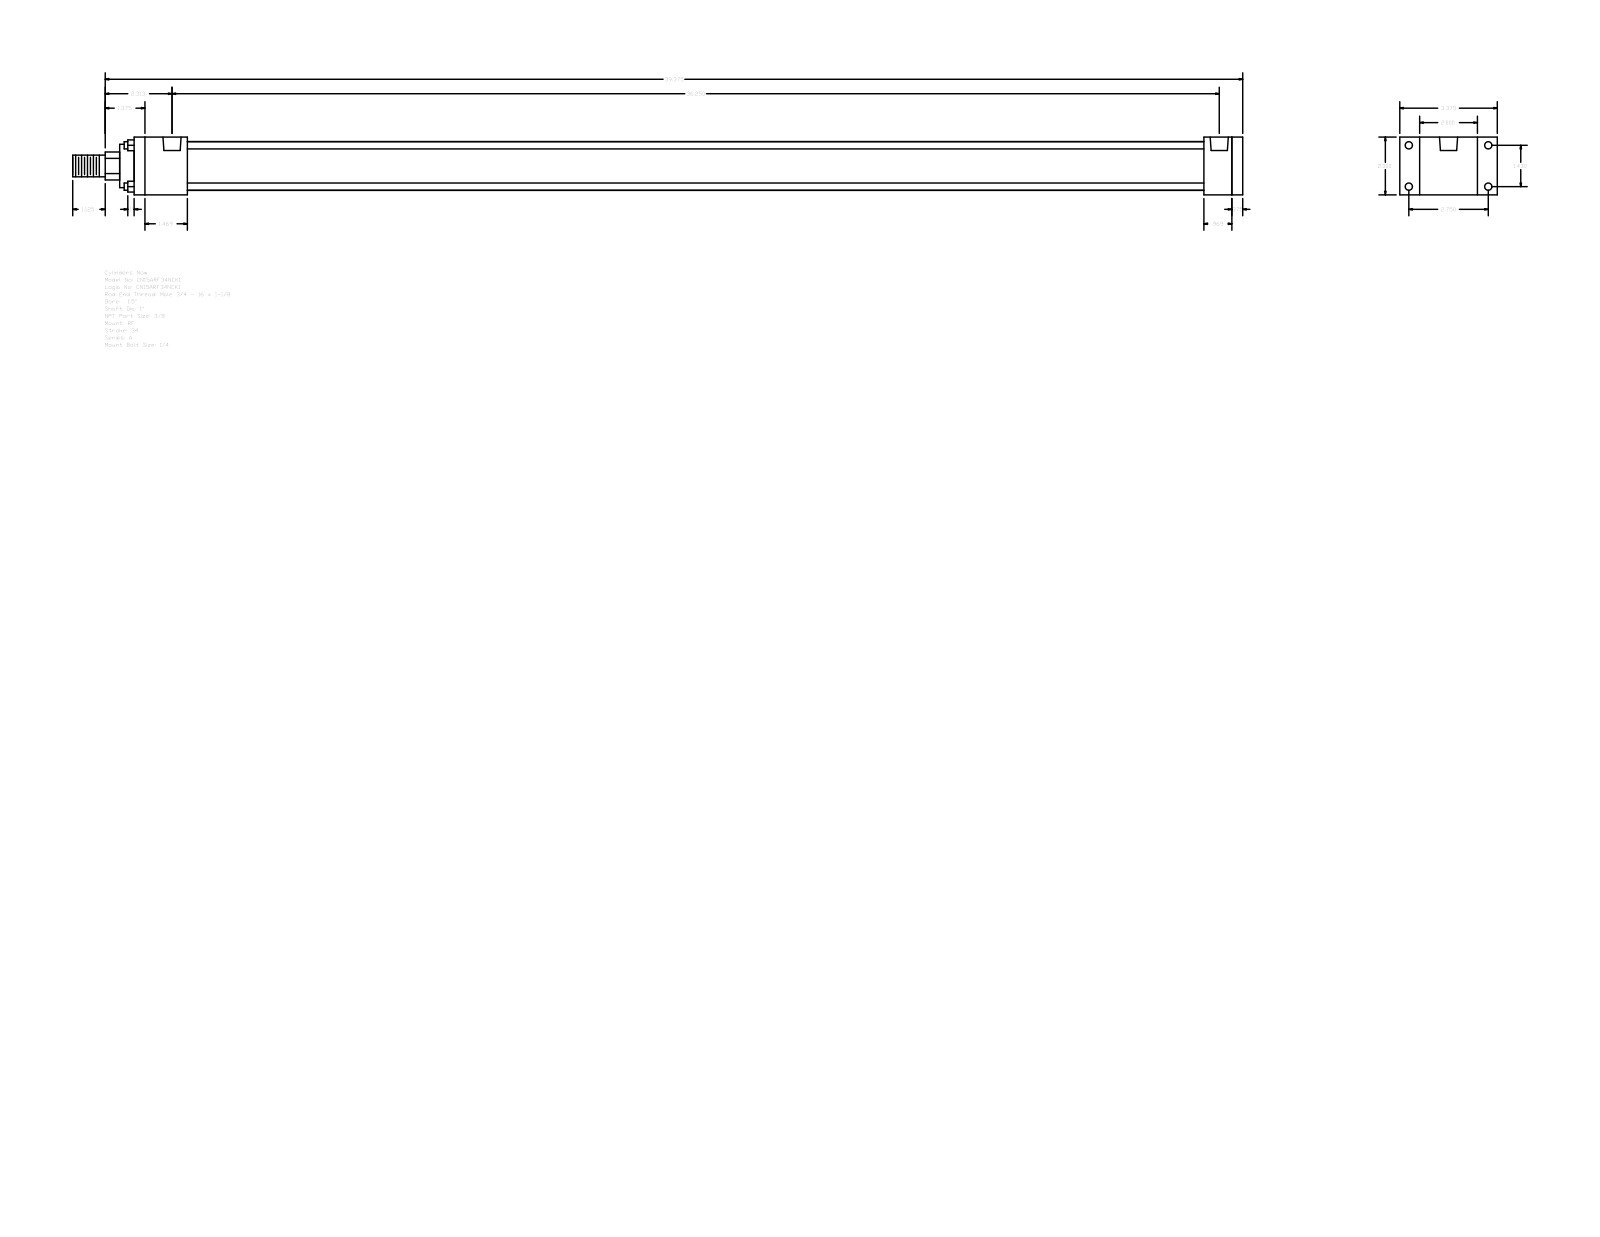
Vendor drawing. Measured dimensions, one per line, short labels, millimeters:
name: A_RF__0150_1
written by: GSSL Pune (CONFIG_CONTROL_DESIGN)
unit: mm
bodies: 0 solids, 92 faces (64 planar, 28 cylindrical, 0 other)
size: 1028.7 × 85.72 × 50.8
holes: 4× ⌀5.56, 4× ⌀6.35, 2× ⌀15.93
bosses: 4× ⌀6.35, 1× ⌀42.93, 1× ⌀38.1, 1× ⌀25.4, 1× ⌀19.05
rounds: 1× R12.29
face distances: 50.8, 9.52, 965.2, 974.72, 940.59, 24.61, 34.13, 46.83, 893.76, 918.37
hole spacings: 3.97, 36.32, 69.84, 78.72, 912.81, 916.78, 920.75
